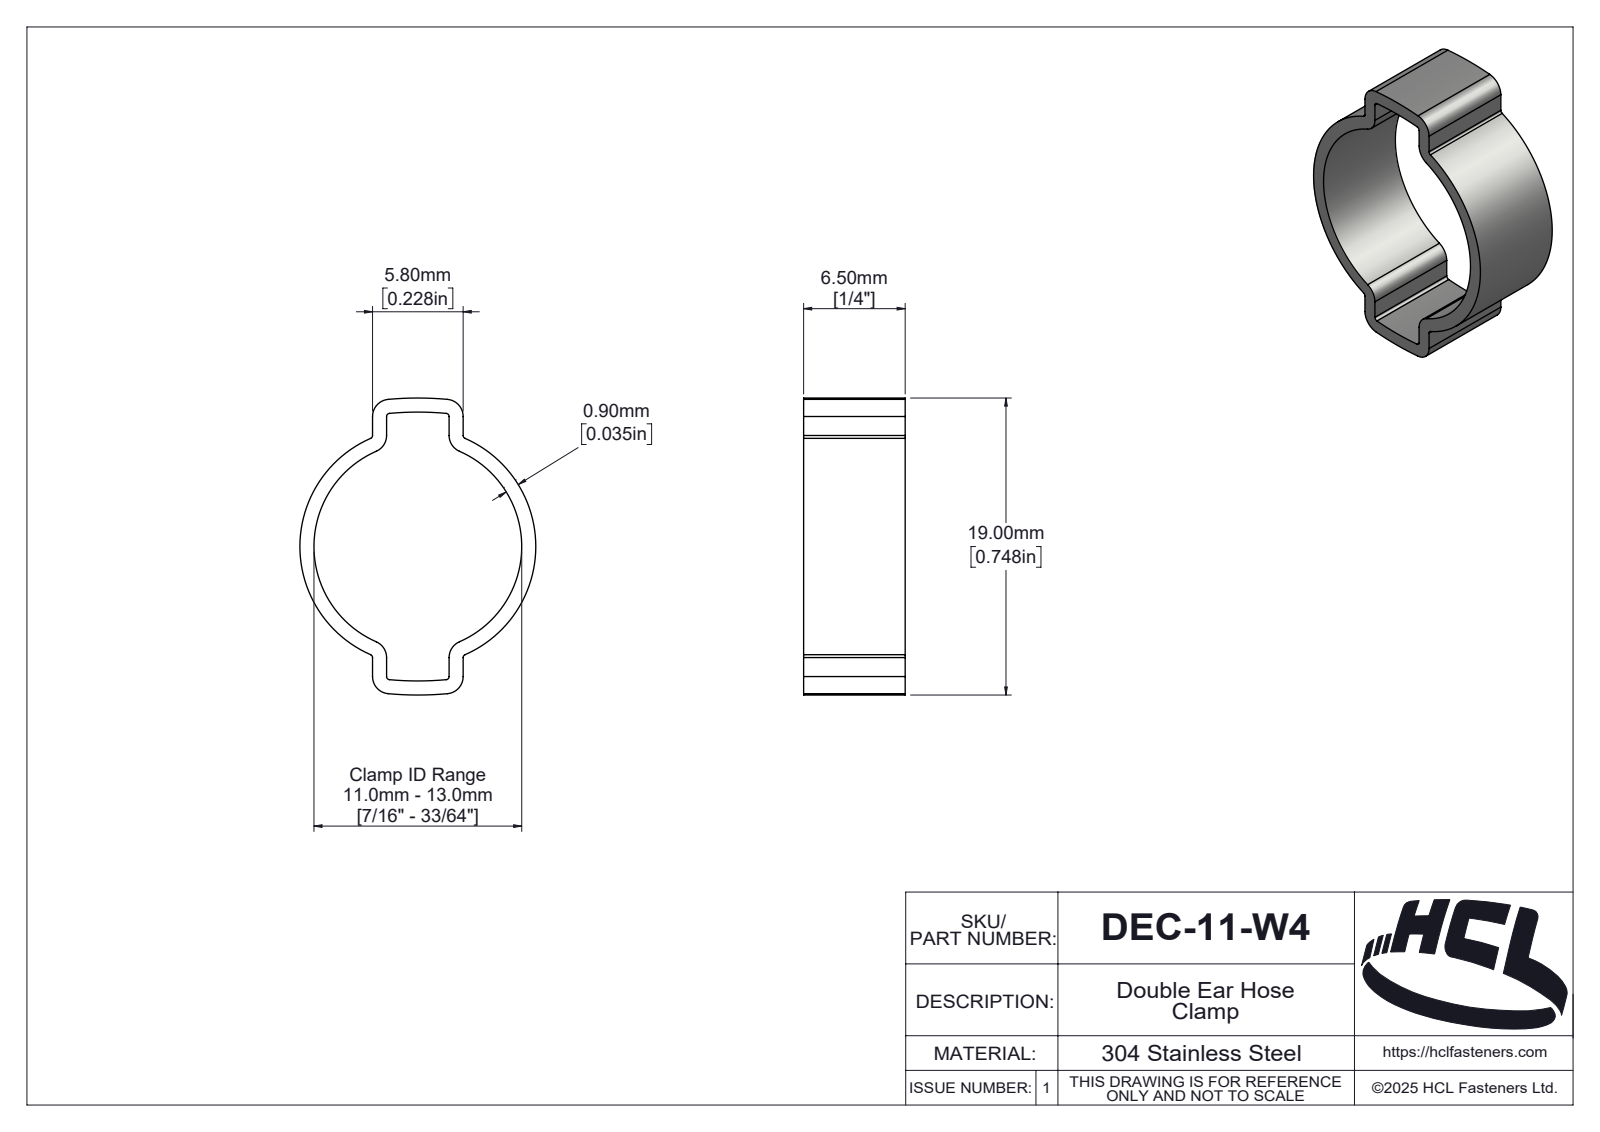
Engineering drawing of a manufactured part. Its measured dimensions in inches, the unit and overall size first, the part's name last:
Units: inches
Overall size (bounding box): 0.748 × 0.594 × 0.256
Partial cylindrical surfaces — rounded edges, fillets, slot ends (radius × count): R0.008 ×8, R0.043 ×8, R0.789 ×2, R0.825 ×2, R0.005 ×1, R0.021 ×1, R0.026 ×1, R0.028 ×1
Main face-to-face distances: 0.256, 0.035, 0.193, 0.228, 0.157, 0.107, 0.072, 0.086, 0.121, 0.111
Volume: 0.019 in³ · Surface area: 1.2 in²
Bodies: 1 solid, 137 faces (12 planar, 76 cylindrical, 49 other)
Part name (STEP PRODUCT): DEC-11-W4
STEP written by: SolidWorks 2025 (AUTOMOTIVE_DESIGN)
